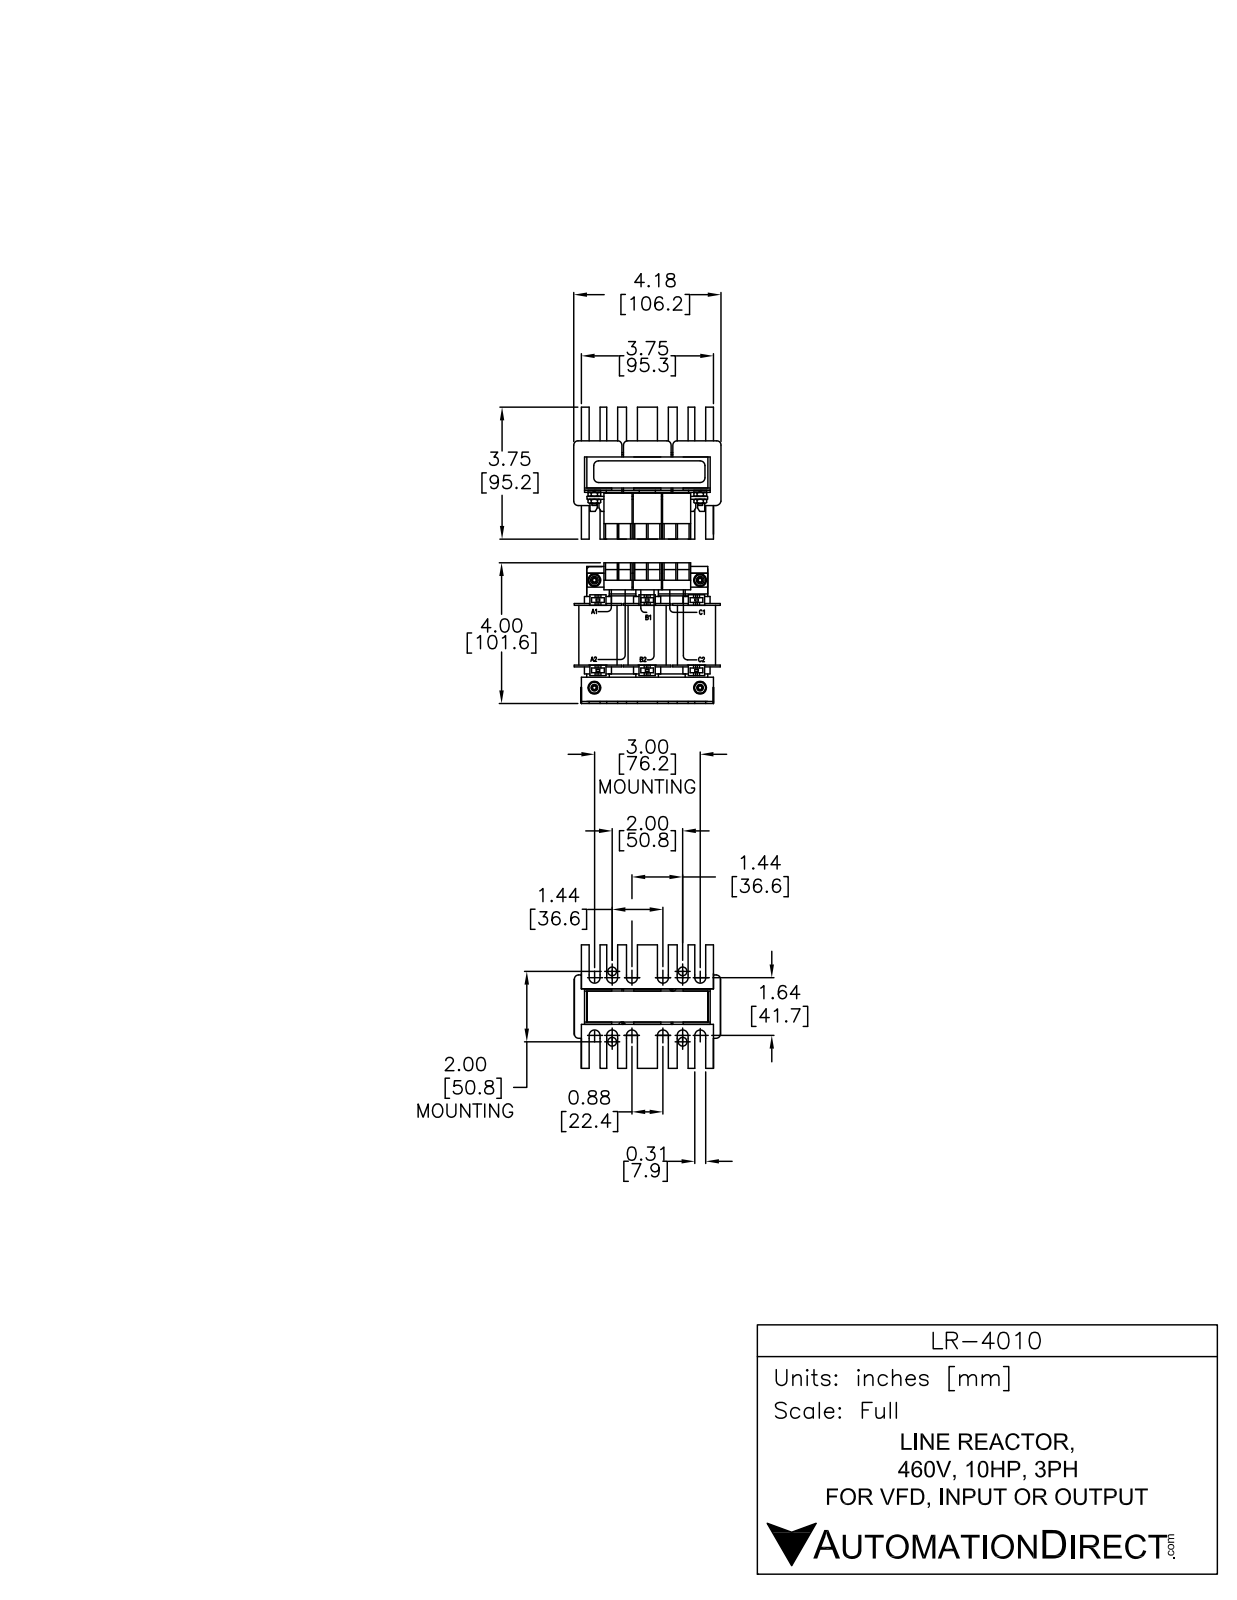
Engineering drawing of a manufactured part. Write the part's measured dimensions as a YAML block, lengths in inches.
part_name: "LR-4010"
step_written_by: "SolidWorks 2011 (AUTOMOTIVE_DESIGN)"
units: inches
bodies: {solids: 17, faces: 941, planar: 743, cylindrical: 198, other: 0}
overall_size: [4.144, 3.874, 3.514]
volume: 16.62
surface_area: 153.8
round_bosses_or_shafts:
  - {diameter: 0.305, count: 4}
  - {diameter: 0.138, count: 4}
partial_cylinders:
  - {radius: 0.157, count: 50}
  - {radius: 0.072, count: 24}
  - {radius: 0.315, count: 12}
  - {radius: 0.118, count: 6}
  - {radius: 0.034, count: 3}
  - {radius: 0.049, count: 2}
face_to_face_distances: [0.197, 0.846, 0.108, 2.008, 1.033, 1.043, 0.295, 1.142, 2.795, 0.098]
